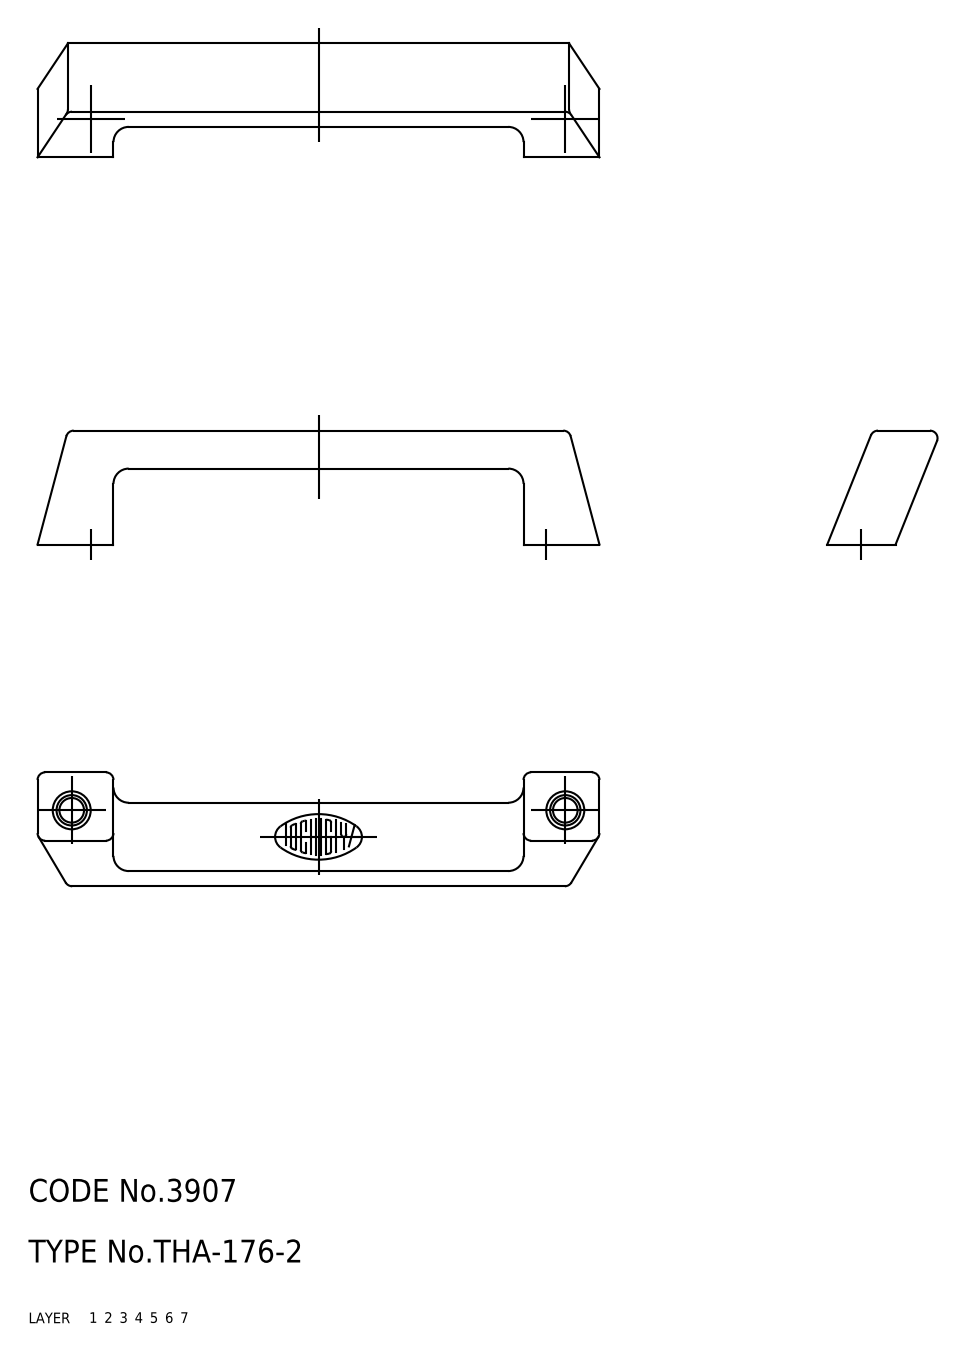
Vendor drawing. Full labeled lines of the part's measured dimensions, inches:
Part name (STEP PRODUCT): pull
STEP written by: CADfix (AUTOMOTIVE_DESIGN)
Units: inches
Bodies: 1 solid, 40 faces (0 planar, 0 cylindrical, 40 other)
Overall size (bounding box): 2.913 × 0.591 × 0.572
Volume: 0.253 in³ · Surface area: 4.19 in²
